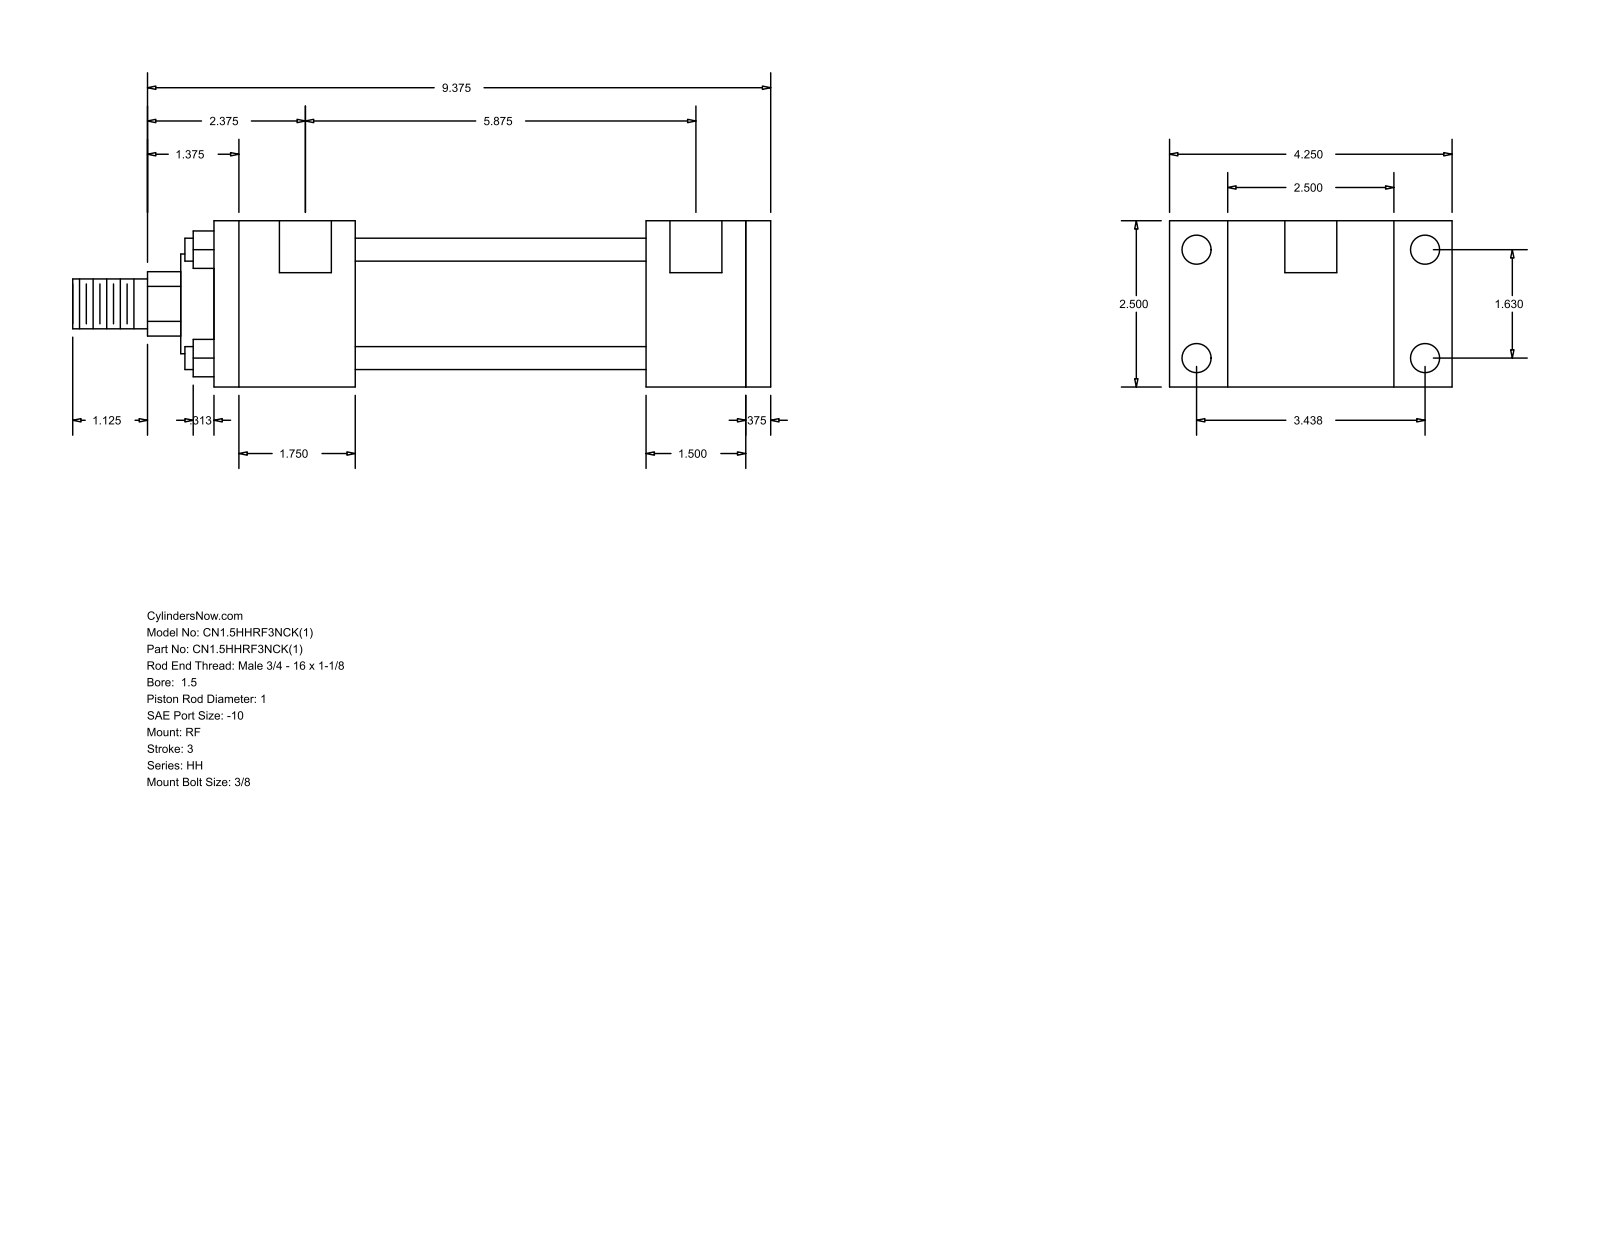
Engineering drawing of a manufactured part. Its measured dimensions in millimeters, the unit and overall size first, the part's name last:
Units: millimetres
Overall size (bounding box): 266.7 × 107.95 × 63.5
Round holes (diameter × count): ⌀5.56 ×4, ⌀11.13 ×4, ⌀19.84 ×2
Round bosses / shafts (diameter × count): ⌀8.76 ×4, ⌀44.45 ×1, ⌀38.1 ×1, ⌀25.4 ×1, ⌀19.05 ×1
Partial cylindrical surfaces — rounded edges, fillets, slot ends (radius × count): R12.29 ×1
Main face-to-face distances: 63.5, 9.52, 38.1, 111.12, 149.22, 158.74, 47.62, 53.98, 165.1, 203.2
Hole centre spacings: 1.59, 41.4, 87.32, 96.64, 150.81, 152.4, 149.22
Bodies: 0 solids, 92 faces (64 planar, 28 cylindrical, 0 other)
Part name (STEP PRODUCT): HH_RF__0150_1
STEP written by: GSSL Pune (CONFIG_CONTROL_DESIGN)
